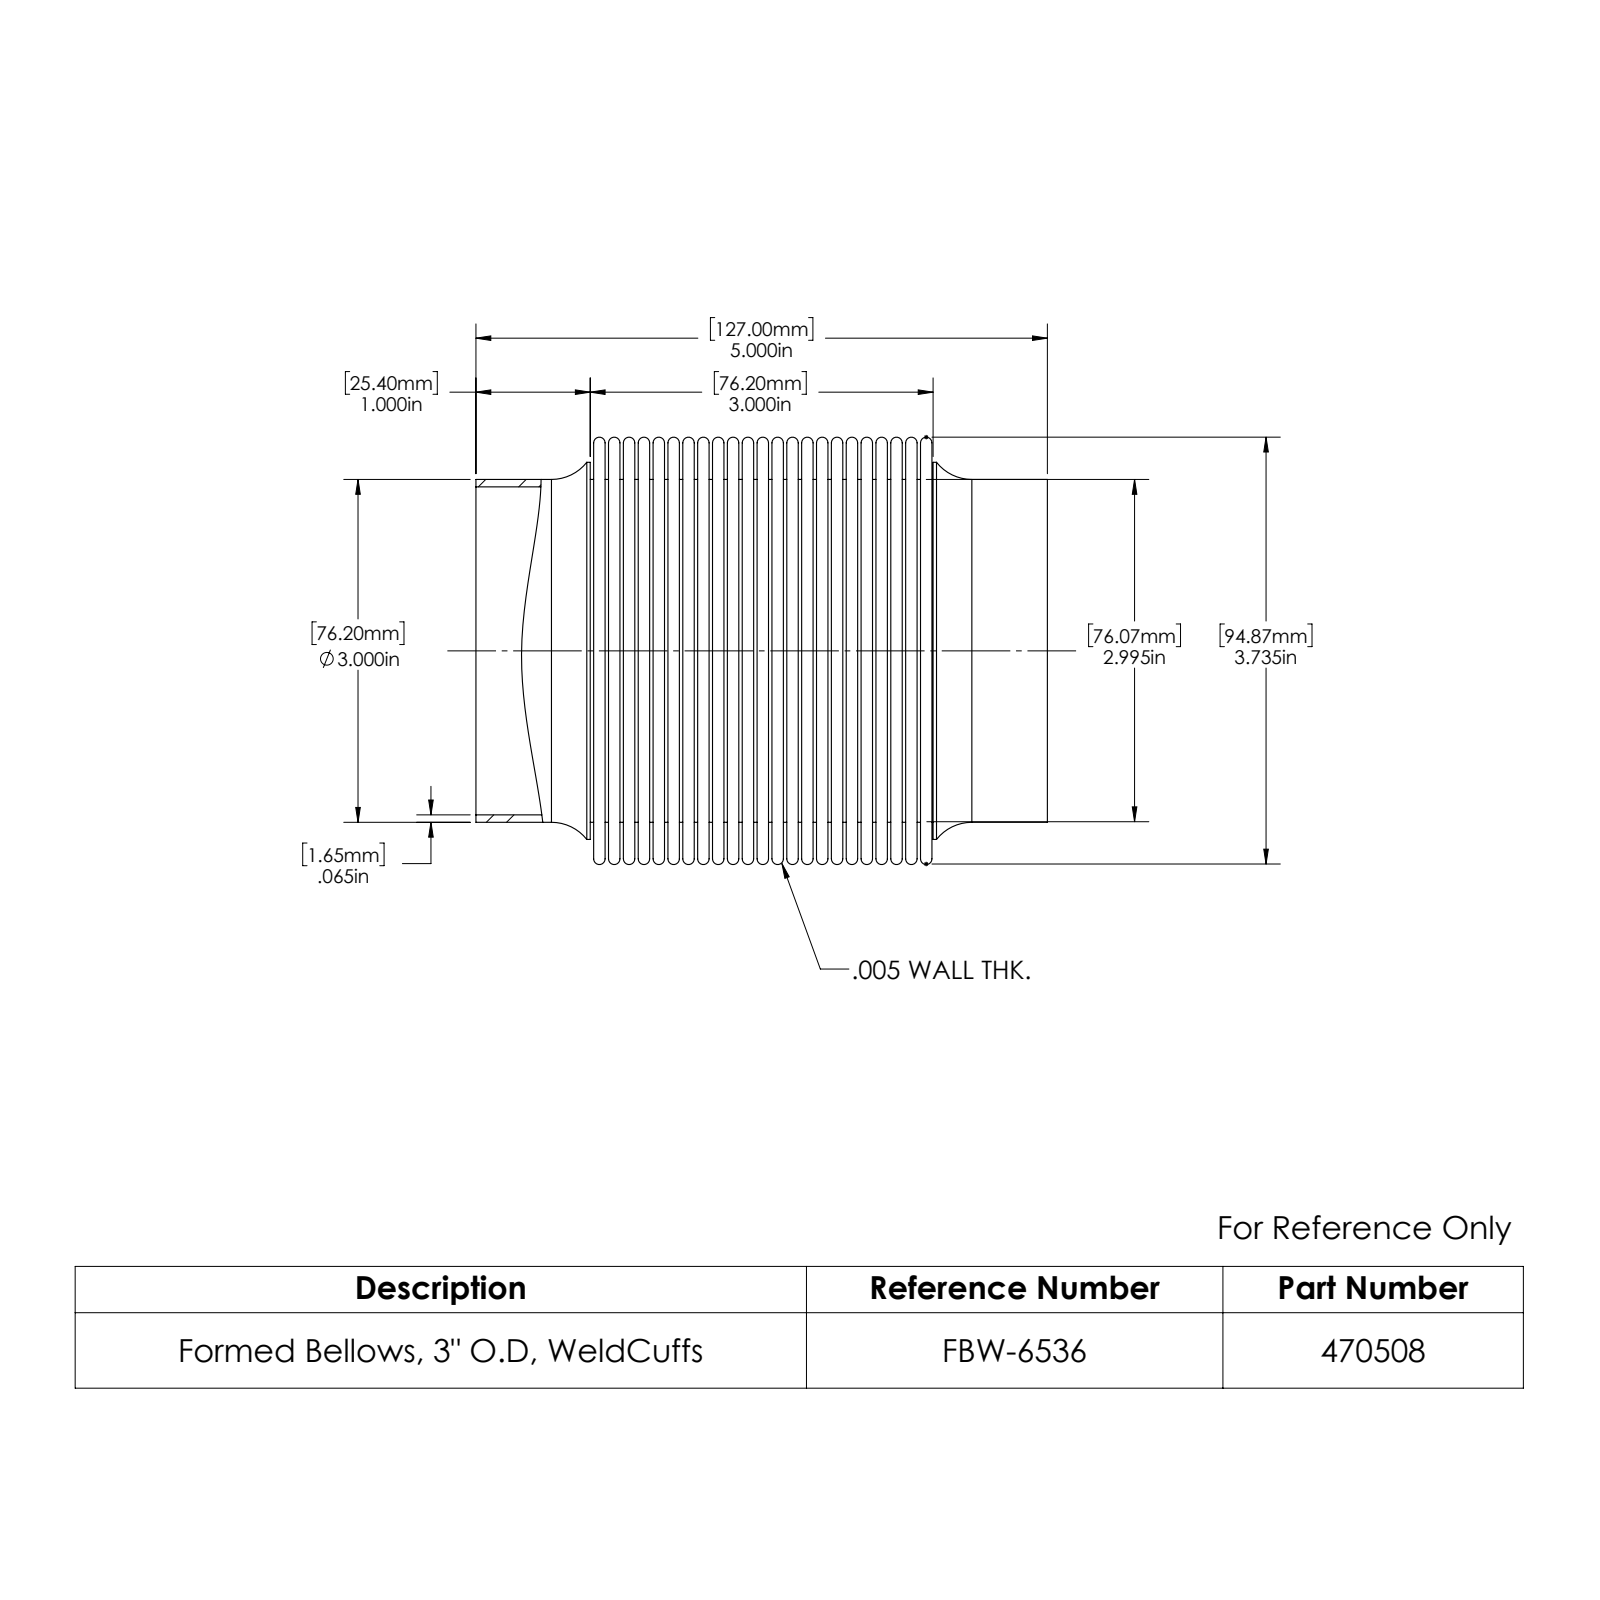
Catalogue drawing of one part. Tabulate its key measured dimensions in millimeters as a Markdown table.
| quantity | value |
| --- | --- |
| part name | 470508 |
| STEP written by | SolidWorks 2022 (AUTOMOTIVE_DESIGN) |
| units | millimeters |
| bodies | 1 solid, 314 faces (102 planar, 116 cylindrical, 96 other) |
| overall size | 127 × 95 × 95 |
| volume | 36 640 mm³ |
| surface area | 292 800 mm² |
| round holes (diameter × count) | 72.9 × 1, 75.9 × 1, 83.6 × 1 |
| round bosses / shafts (diameter × count) | 83.8 × 1, 76.2 × 1 |
| main face-to-face distances | 3.3, 16.5, 13.2, 19.8, 33, 6.6, 29.7, 9.9, 9.9, 36.3 |
